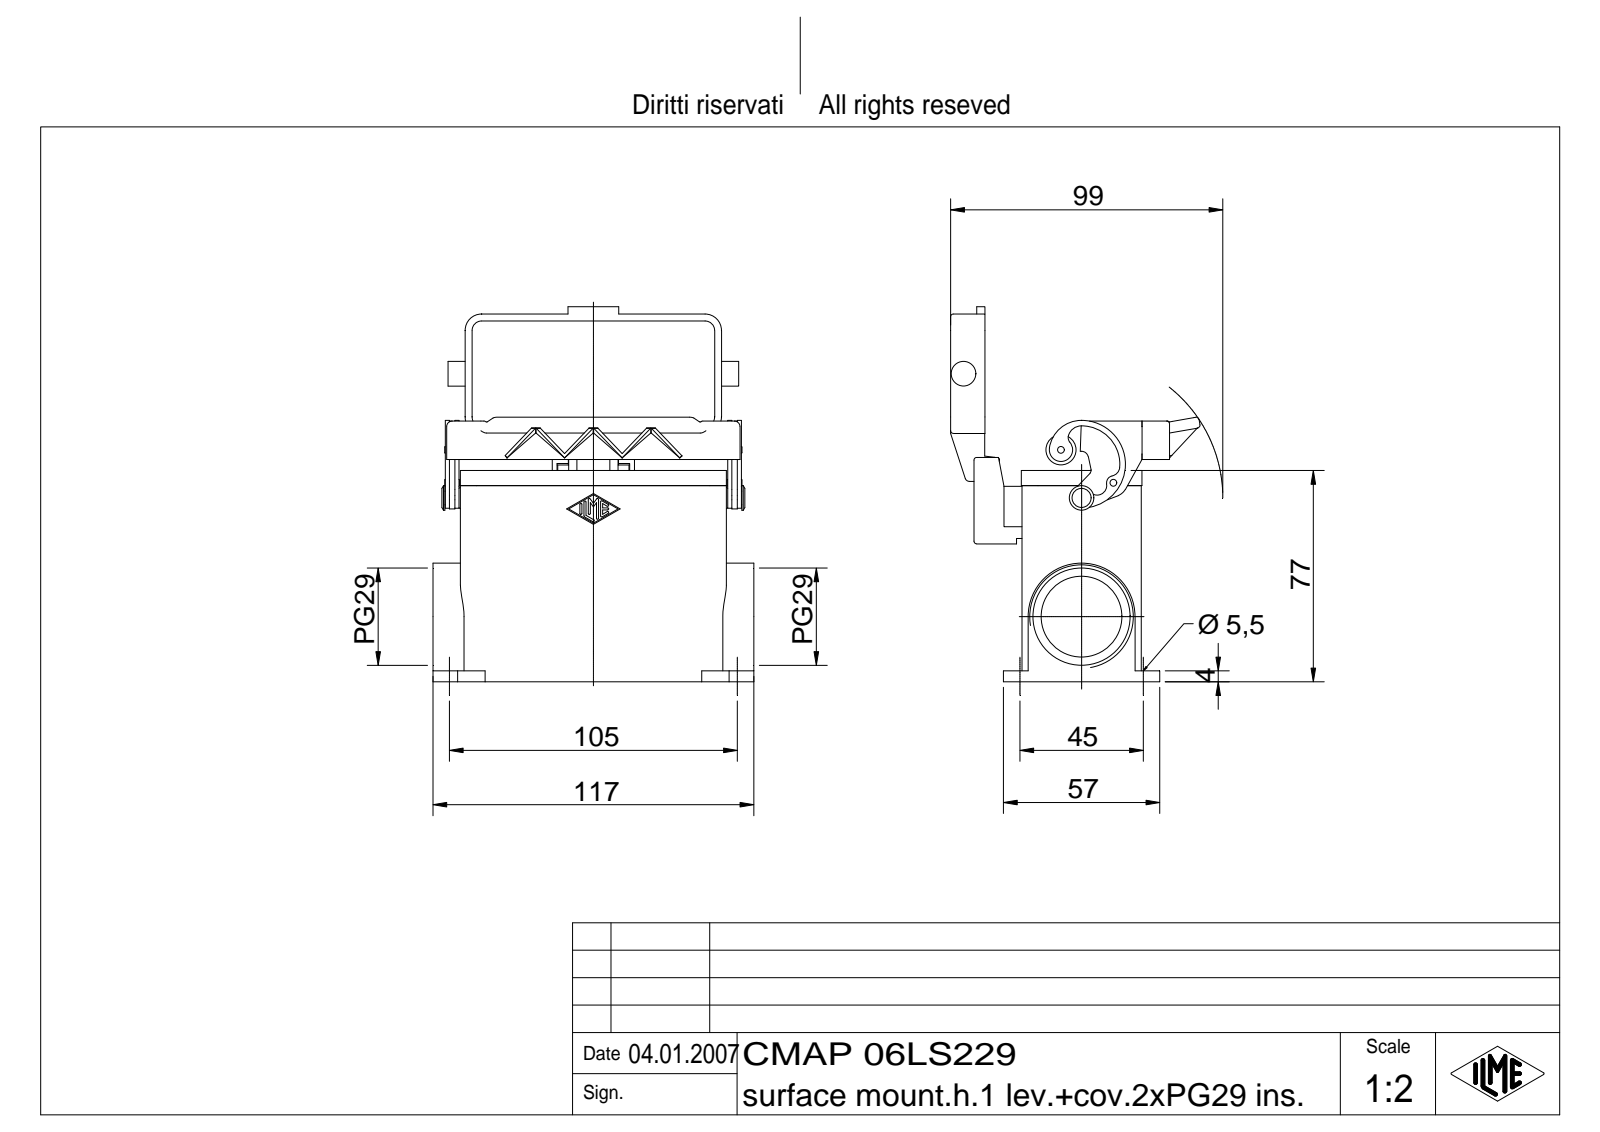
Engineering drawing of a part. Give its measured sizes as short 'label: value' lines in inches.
name: CMAP 06LS229
written by: Autodesk Inventor 7 (AUTOMOTIVE_DESIGN)
unit: in
bodies: 6 solids, 611 faces (265 planar, 182 cylindrical, 164 other)
size: 5.382 × 4.606 × 3.581
volume: 9.449 in³; area: 132.9 in²
holes: 4× ⌀0.217, 1× ⌀0.079, 1× ⌀0.157, 1× ⌀1.161, 1× ⌀1.397
bosses: 2× ⌀0.354, 2× ⌀0.197, 1× ⌀0.433, 1× ⌀0.276, 1× ⌀0.157, 1× ⌀0.118, 1× ⌀0.098
rounds: 18× R0.039, 14× R0.015, 12× R0.079, 12× R0.236, 6× R0.059, 6× R0.138, 4× R0.118, 3× R0.02
face distances: 0.118, 1.594, 1.713, 0.157, 1.476, 1.024, 2.618, 2.736, 1.142, 0.886
hole spacings: 1.772, 4.134, 4.498, 1.973
